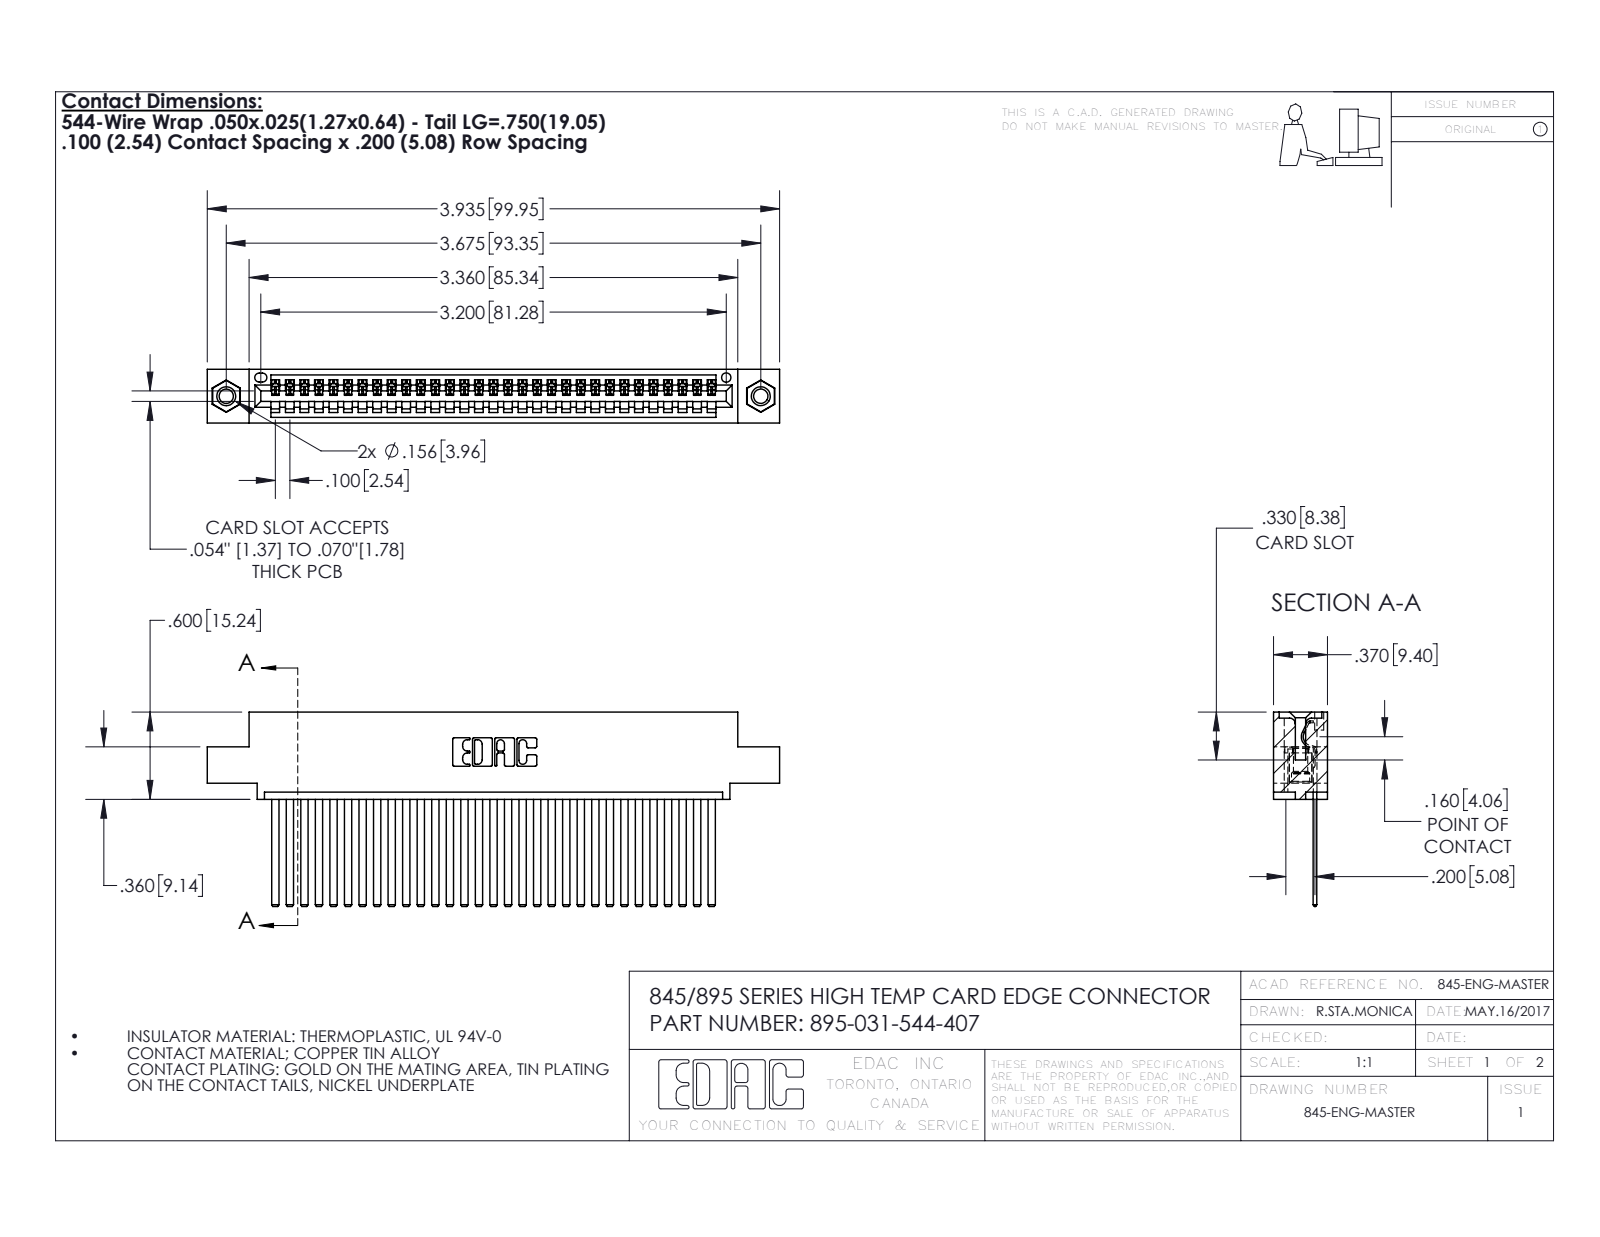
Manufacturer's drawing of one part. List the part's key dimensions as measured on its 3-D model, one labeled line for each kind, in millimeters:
Part name (STEP PRODUCT): 395-031-544-407; 345 Part_0.110 Offset - 0.156 Dia-TI; 345-250-001_345-250-005-103; 345-292-001_345-293-144
STEP written by: SolidWorks 2016 (CONFIG_CONTROL_DESIGN)
Units: millimetres
Bodies: 34 solids, 1802 faces (1232 planar, 554 cylindrical, 16 other)
Overall size (bounding box): 99.9 × 34 × 9.4
Volume: 9 670 mm³ · Surface area: 13 900 mm²
Round holes (diameter × count): ⌀2.5 ×2, ⌀3.2 ×2, ⌀4 ×2, ⌀1.6 ×1
Round bosses / shafts (diameter × count): ⌀3.9 ×2
Partial cylindrical surfaces — rounded edges, fillets, slot ends (radius × count): R0.2 ×62, R0.3 ×22, R0.2 ×6, R0.8 ×6, R0.7 ×3, R0.8 ×2, R1 ×2, R0.4 ×1
Main face-to-face distances: 1.8, 7.6, 0.6, 2.5, 6.9, 9.4, 5.1, 5.7, 3.8, 1.8
Hole centre spacings: 6.9, 87.4, 93.3
